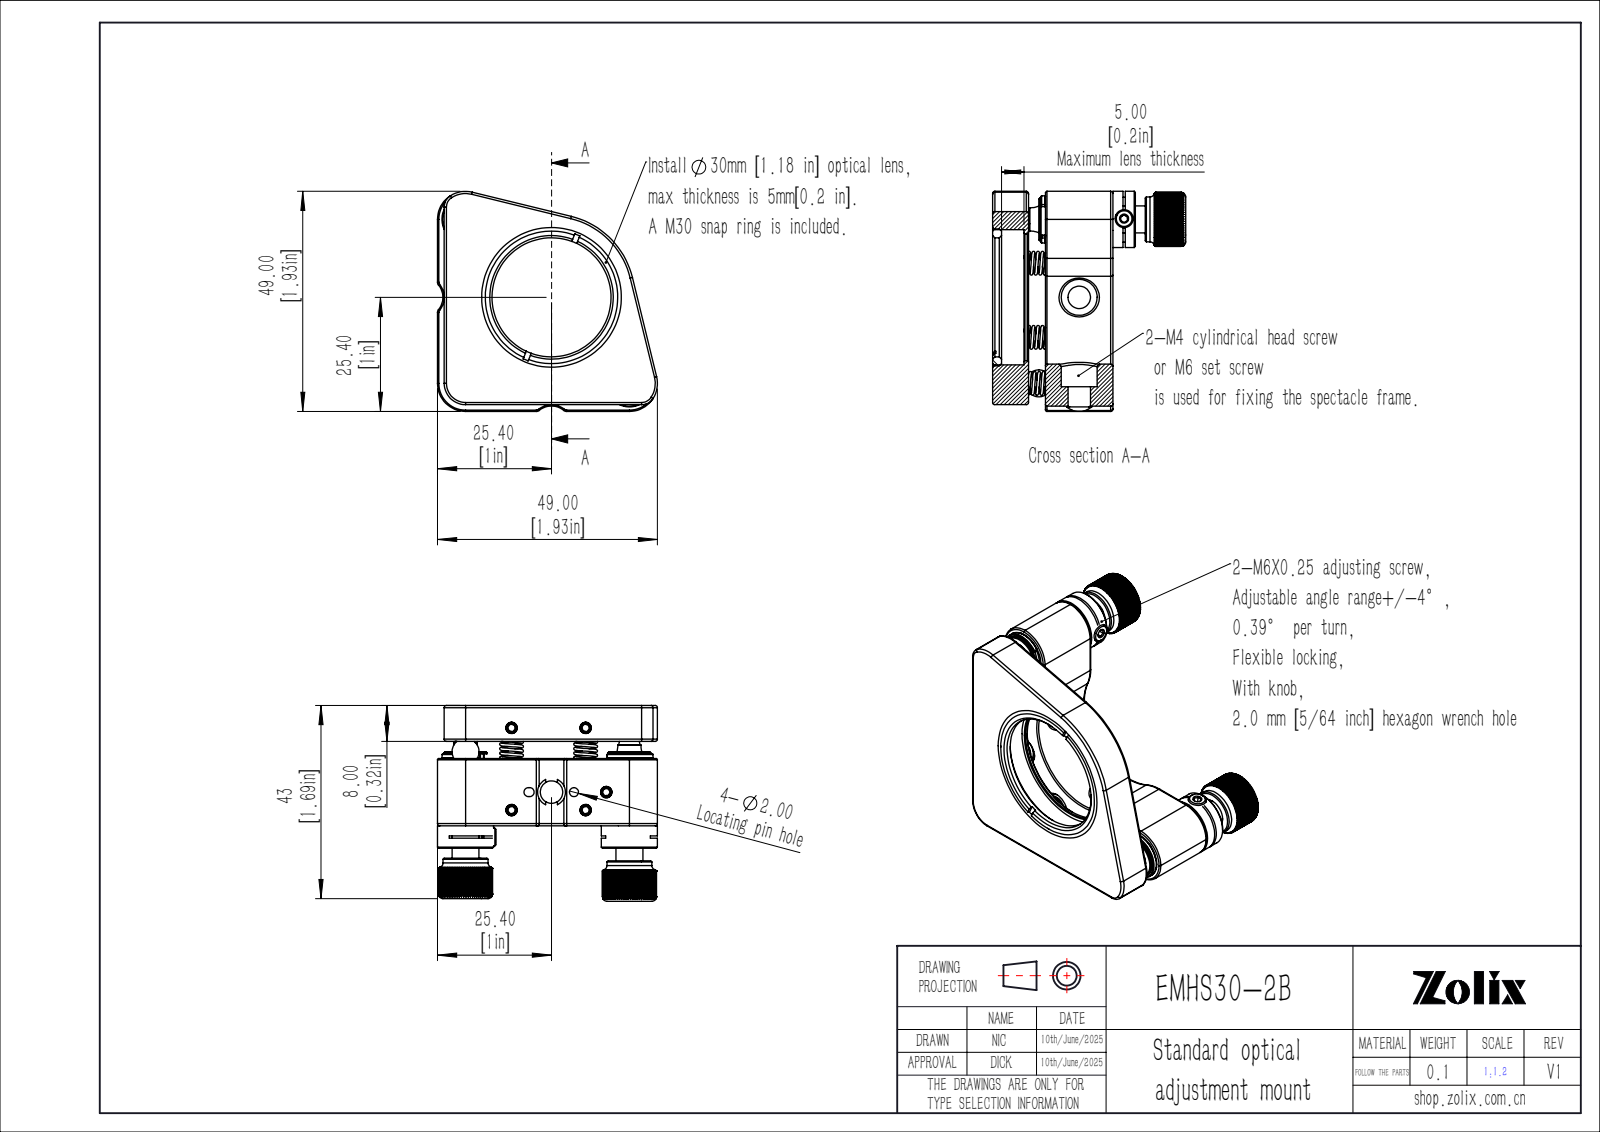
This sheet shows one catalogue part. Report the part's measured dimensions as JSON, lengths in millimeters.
{"part_name": "EMHS30-2B", "step_written_by": "SolidWorks 2020 (CONFIG_CONTROL_DESIGN)", "units": "millimeters", "bodies": {"solids": 0, "faces": 999, "planar": 455, "cylindrical": 299, "other": 245}, "overall_size": [49, 49, 43.6], "round_holes": [[6, 5], [2, 2], [5, 2], [8, 2], [4, 1], [4.6, 1], [6.3, 1], [10, 1], [26.5, 1], [28.2, 1], [30.1, 1]], "round_bosses_or_shafts": [[3, 8], [4, 3], [12.5, 2], [9.5, 2], [1.5, 2], [10, 1], [8, 1], [6, 1]], "partial_cylinders_radius": [[0.5, 12], [1, 8], [0.3, 6], [0.8, 4], [3, 2], [3.1, 2], [4.35, 2], [5.25, 2]], "face_to_face_distances": [8, 26.8, 18.8, 11.8, 3.8, 1.5, 15, 2.25, 2.75, 11], "hole_center_spacings": [5, 9.75, 16.5, 20.6, 21.12, 25.84, 26.25, 28.65]}
